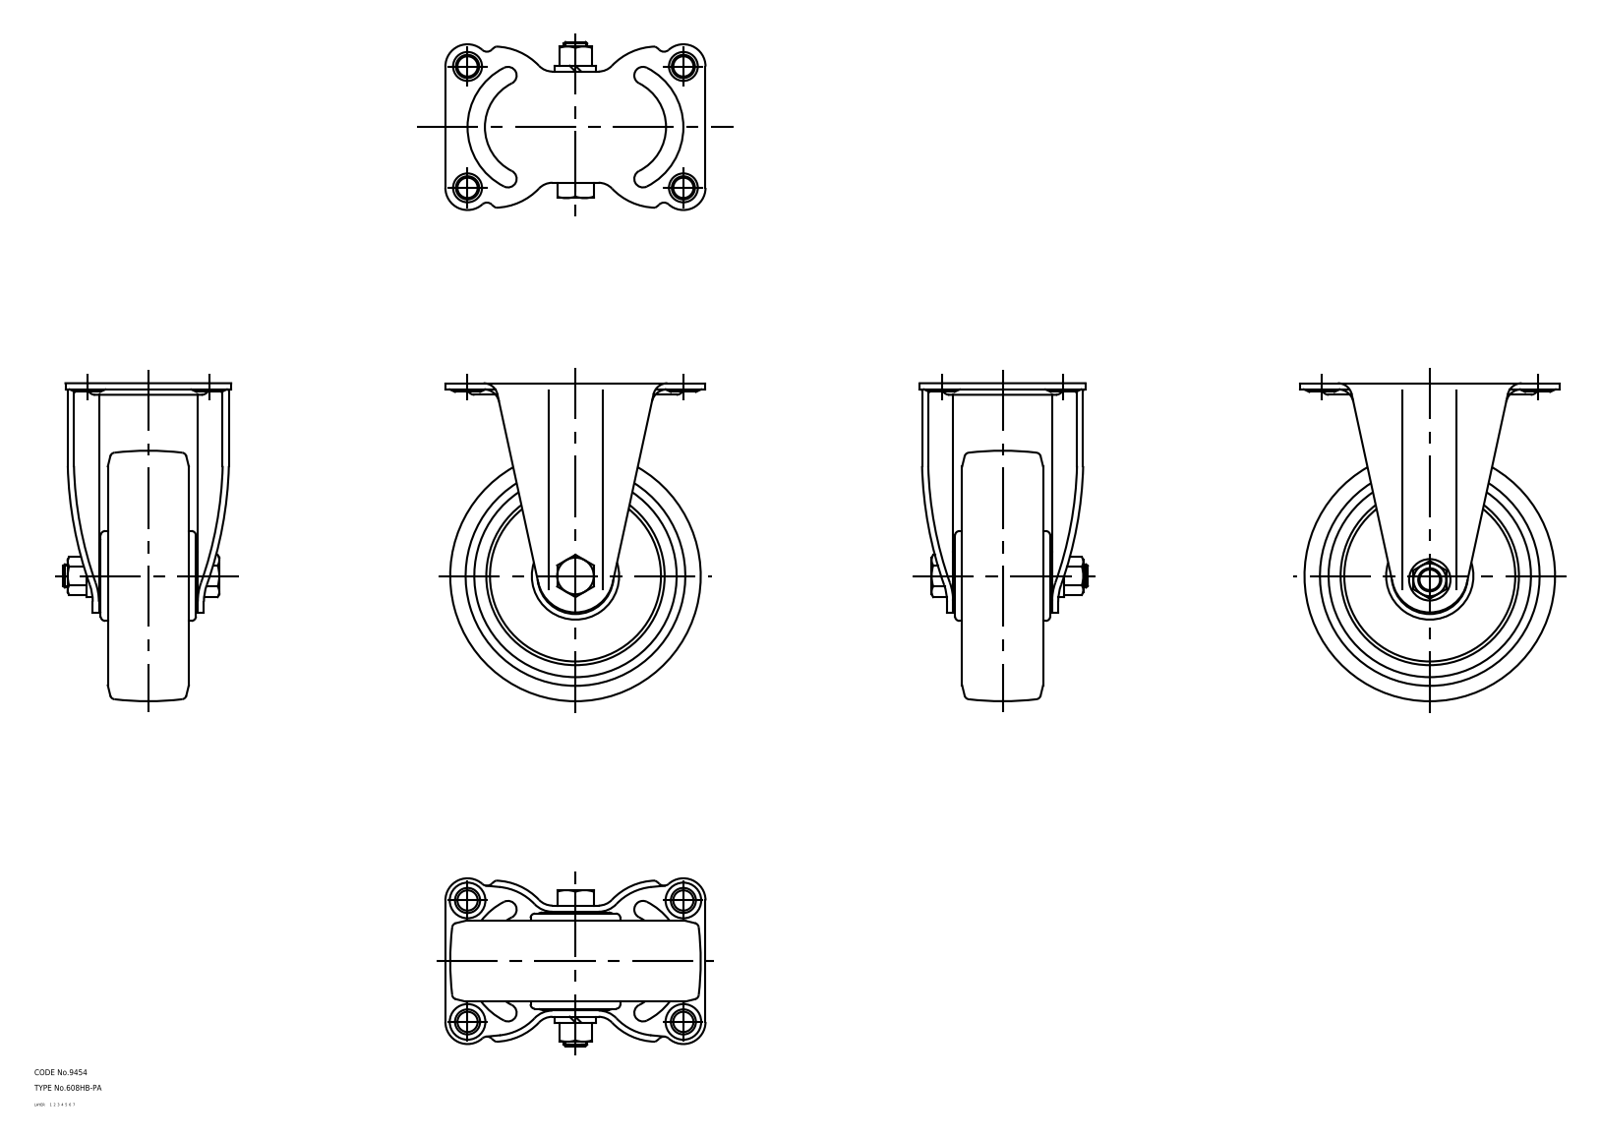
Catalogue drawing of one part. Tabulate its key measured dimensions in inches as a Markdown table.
| quantity | value |
| --- | --- |
| part name | 67122919; 67122932; 67122945 |
| STEP written by | CADfix (AUTOMOTIVE_DESIGN) |
| units | inches |
| bodies | 3 solids, 214 faces (0 planar, 0 cylindrical, 214 other) |
| overall size | 6.496 × 5.315 × 3.431 |
| volume | 34.77 in³ |
| surface area | 161.4 in² |
